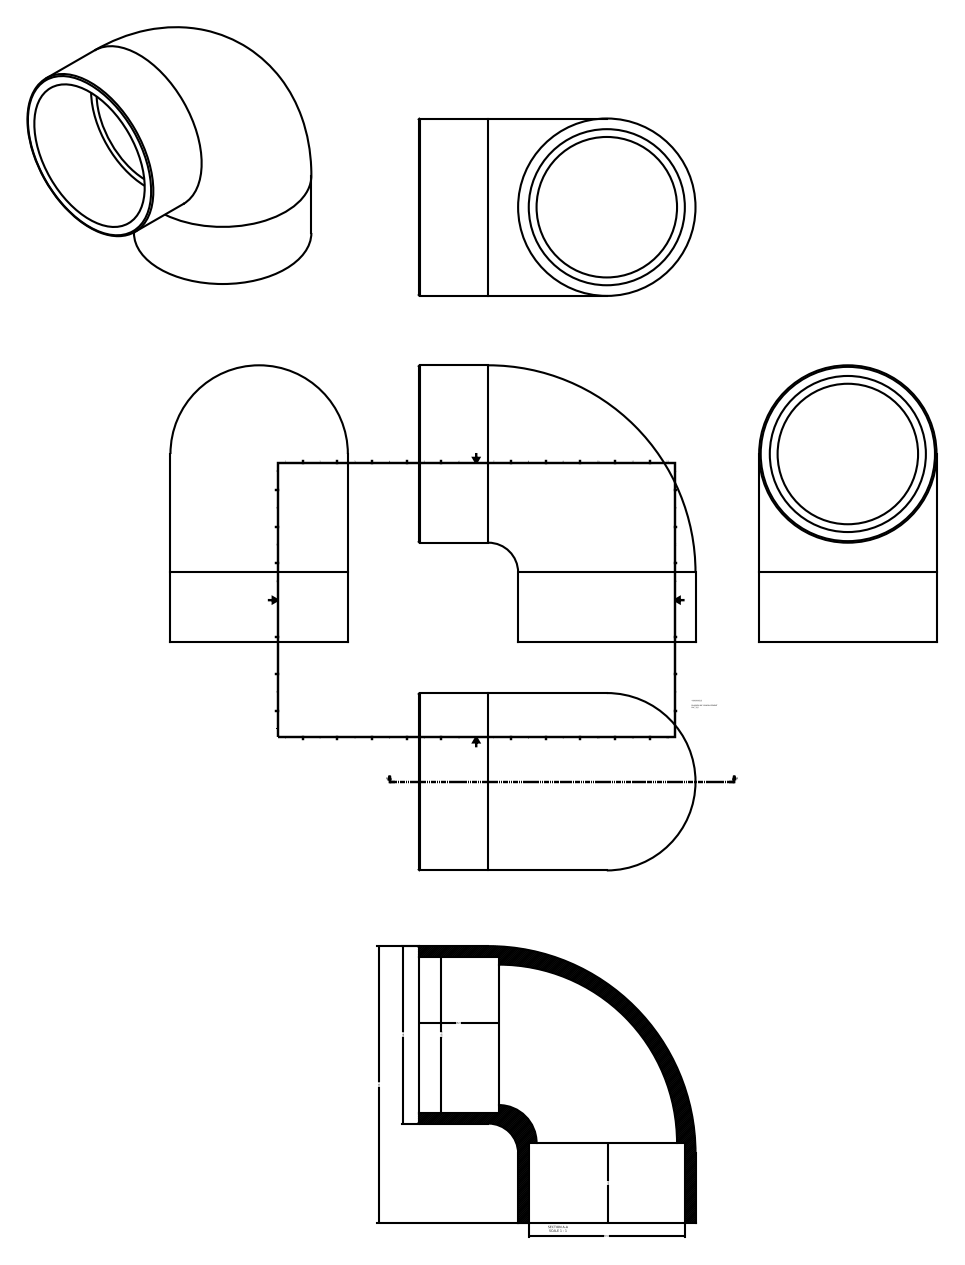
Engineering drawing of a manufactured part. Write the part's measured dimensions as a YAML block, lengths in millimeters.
part_name: "(_AS)050500315"
step_written_by: "Autodesk Inventor 2015 (AUTOMOTIVE_DESIGN)"
units: millimeters
bodies: {solids: 1, faces: 11, planar: 4, cylindrical: 4, other: 3}
overall_size: [559, 559, 358]
volume: 19310000
surface_area: 1439000
round_holes:
  - {diameter: 315, count: 2}
round_bosses_or_shafts:
  - {diameter: 358, count: 2}
face_to_face_distances: [162]
